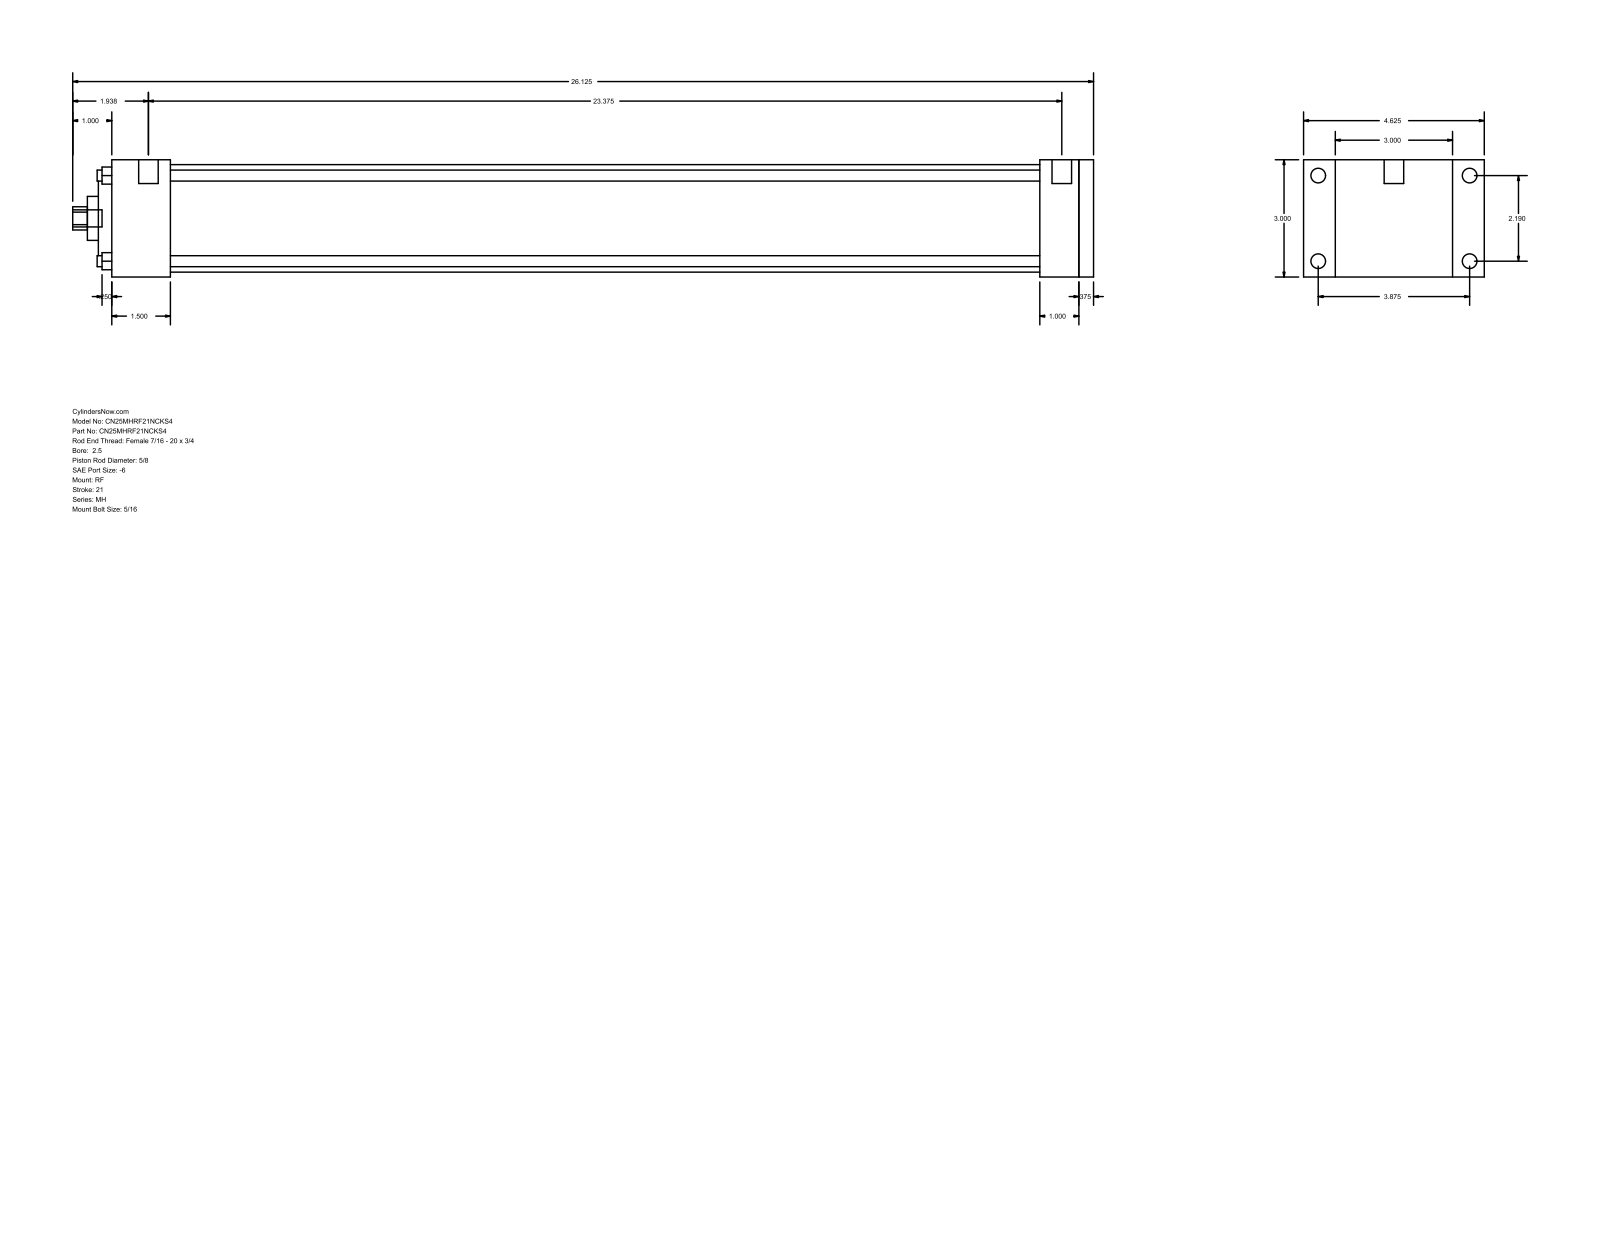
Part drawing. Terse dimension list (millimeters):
name: MH_RF__0250_0.625
written by: GSSL Pune (CONFIG_CONTROL_DESIGN)
unit: mm
bodies: 0 solids, 94 faces (65 planar, 29 cylindrical, 0 other)
size: 663.58 × 117.47 × 76.2
holes: 4× ⌀7.14, 1× ⌀15.88, 1× ⌀28.57, 1× ⌀55.55, 1× ⌀69.85
bosses: 4× ⌀9.53, 4× ⌀5.56, 2× ⌀12.7, 1× ⌀11.11
rounds: 1× R7.54
face distances: 76.2, 9.53, 638.18, 628.65, 25.4, 603.25, 34.93, 38.1, 565.15, 590.55
hole spacings: 39.33, 55.62, 78.66
